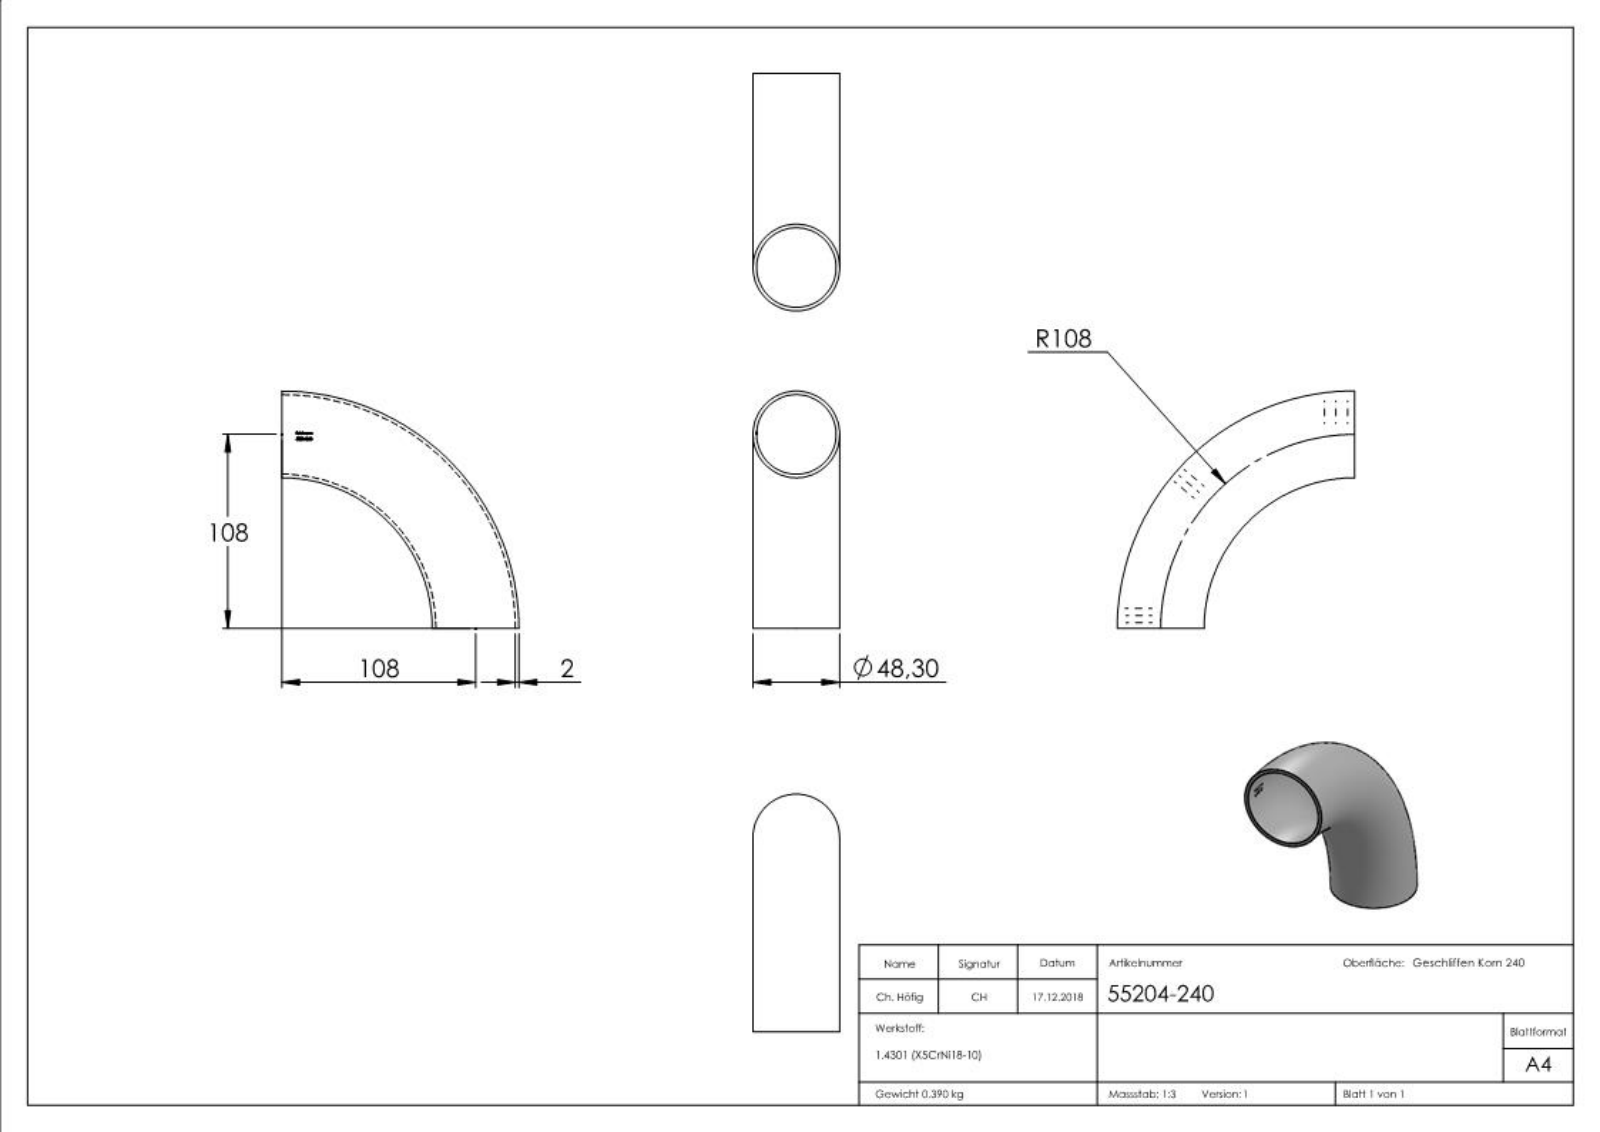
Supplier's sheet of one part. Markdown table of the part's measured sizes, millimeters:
| quantity | value |
| --- | --- |
| part name | 55204-240 |
| STEP written by | SolidWorks 2015 (CONFIG_CONTROL_DESIGN) |
| units | millimeters |
| bodies | 1 solid, 232 faces (110 planar, 0 cylindrical, 122 other) |
| overall size | 132.15 × 132.15 × 48.3 |
| volume | 49 351 mm³ |
| surface area | 49 944 mm² |
| main face-to-face distances | 2.97, 1.32, 1.26, 0.33, 2.65, 0.39, 1.38, 3.66, 0.88, 3.27 |
